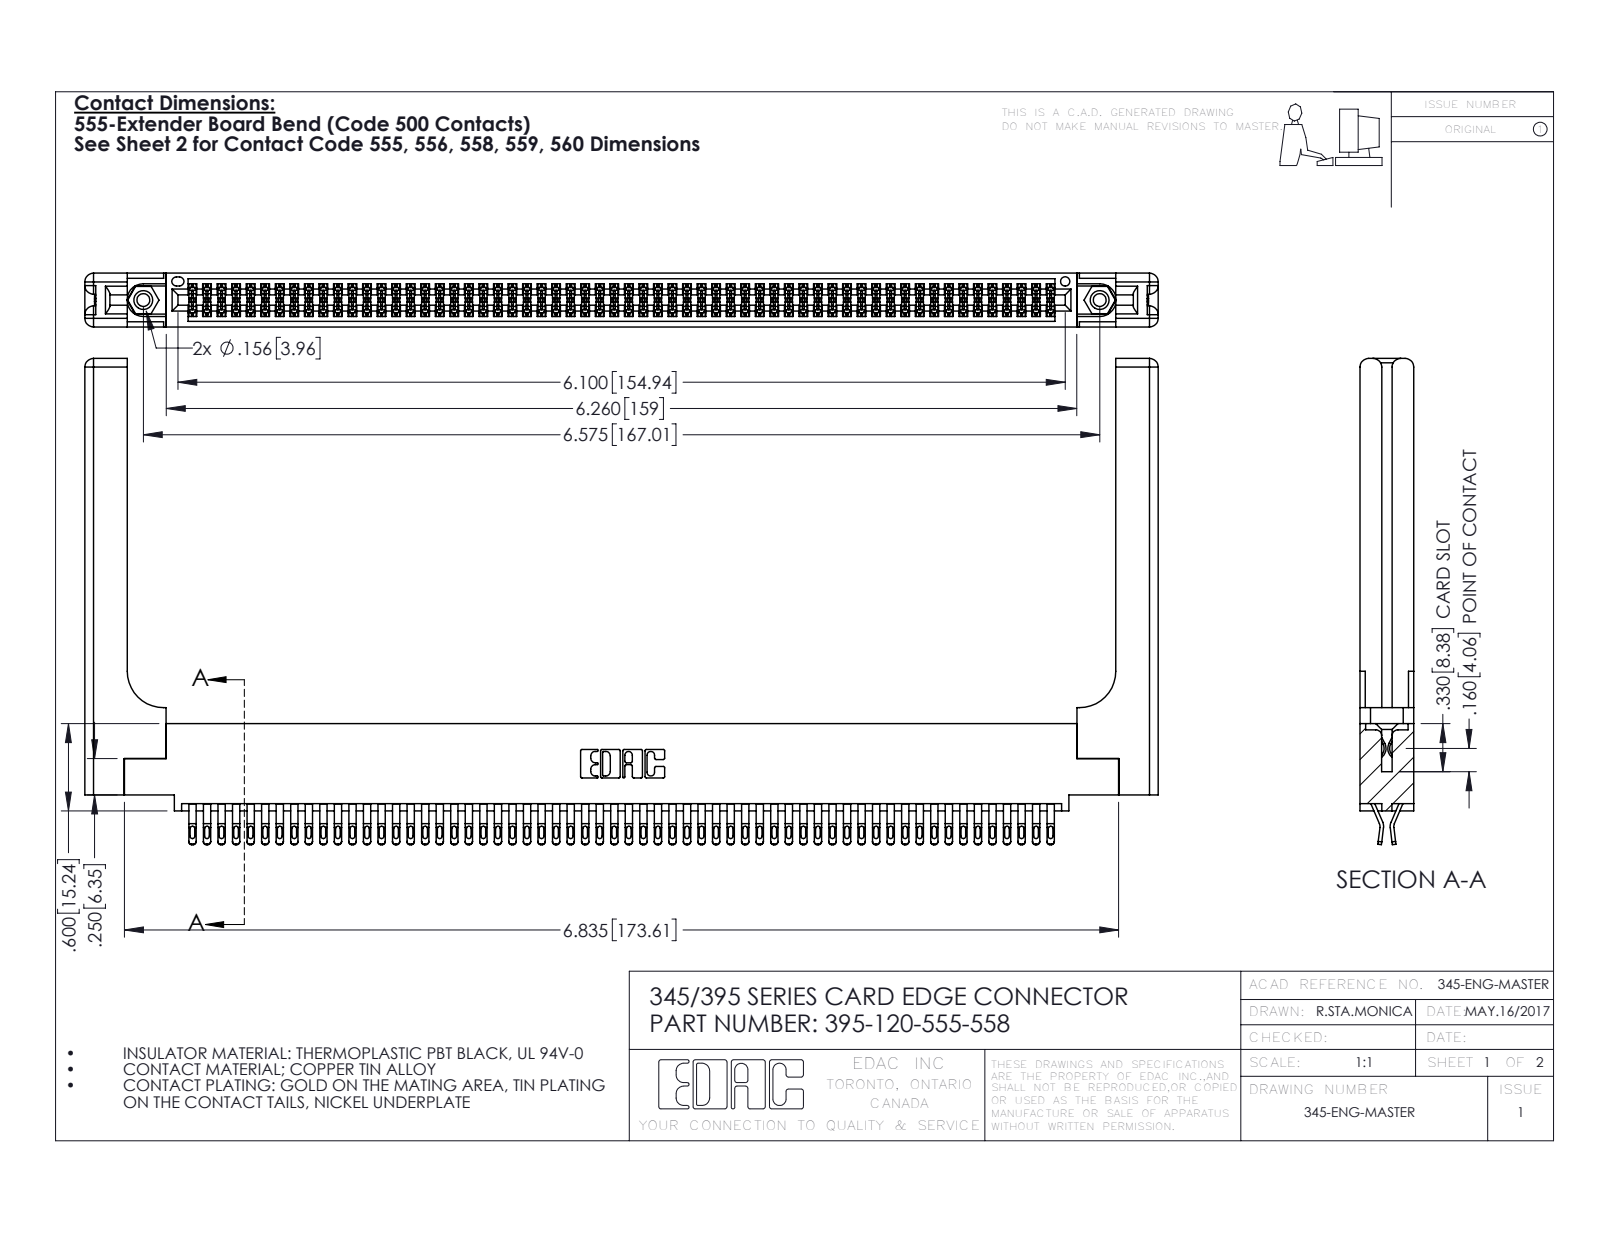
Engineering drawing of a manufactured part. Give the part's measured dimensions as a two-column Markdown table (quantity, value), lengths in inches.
| quantity | value |
| --- | --- |
| part name | 345-250-001_345-250-001-102; 395-120-555-558; 345 Part_0.110 Offset - 0.156 Dia-TH; 345-220-058_345-220-058 (+1 more) |
| STEP written by | SolidWorks 2016 (CONFIG_CONTROL_DESIGN) |
| units | inches |
| bodies | 125 solids, 7106 faces (3952 planar, 3094 cylindrical, 60 other) |
| overall size | 7.379 × 3.342 × 0.37 |
| volume | 1.655 in³ |
| surface area | 53.13 in² |
| round holes (diameter × count) | 0.089 × 2, 0.125 × 2, 0.156 × 2, 0.064 × 1 |
| round bosses / shafts (diameter × count) | 0.155 × 2 |
| partial cylindrical surfaces (radius × count) | 0.016 × 300, 0.02 × 240, 0.006 × 180, 0.01 × 22, 0.06 × 16, 0.007 × 6, 0.031 × 6, 0.026 × 3 |
| main face-to-face distances | 0.072, 0.298, 0.37, 0.025, 0.098, 0.272, 0.2, 0.225, 0.148, 0.15 |
| hole center spacings | 0.27, 6.339, 6.575 |
